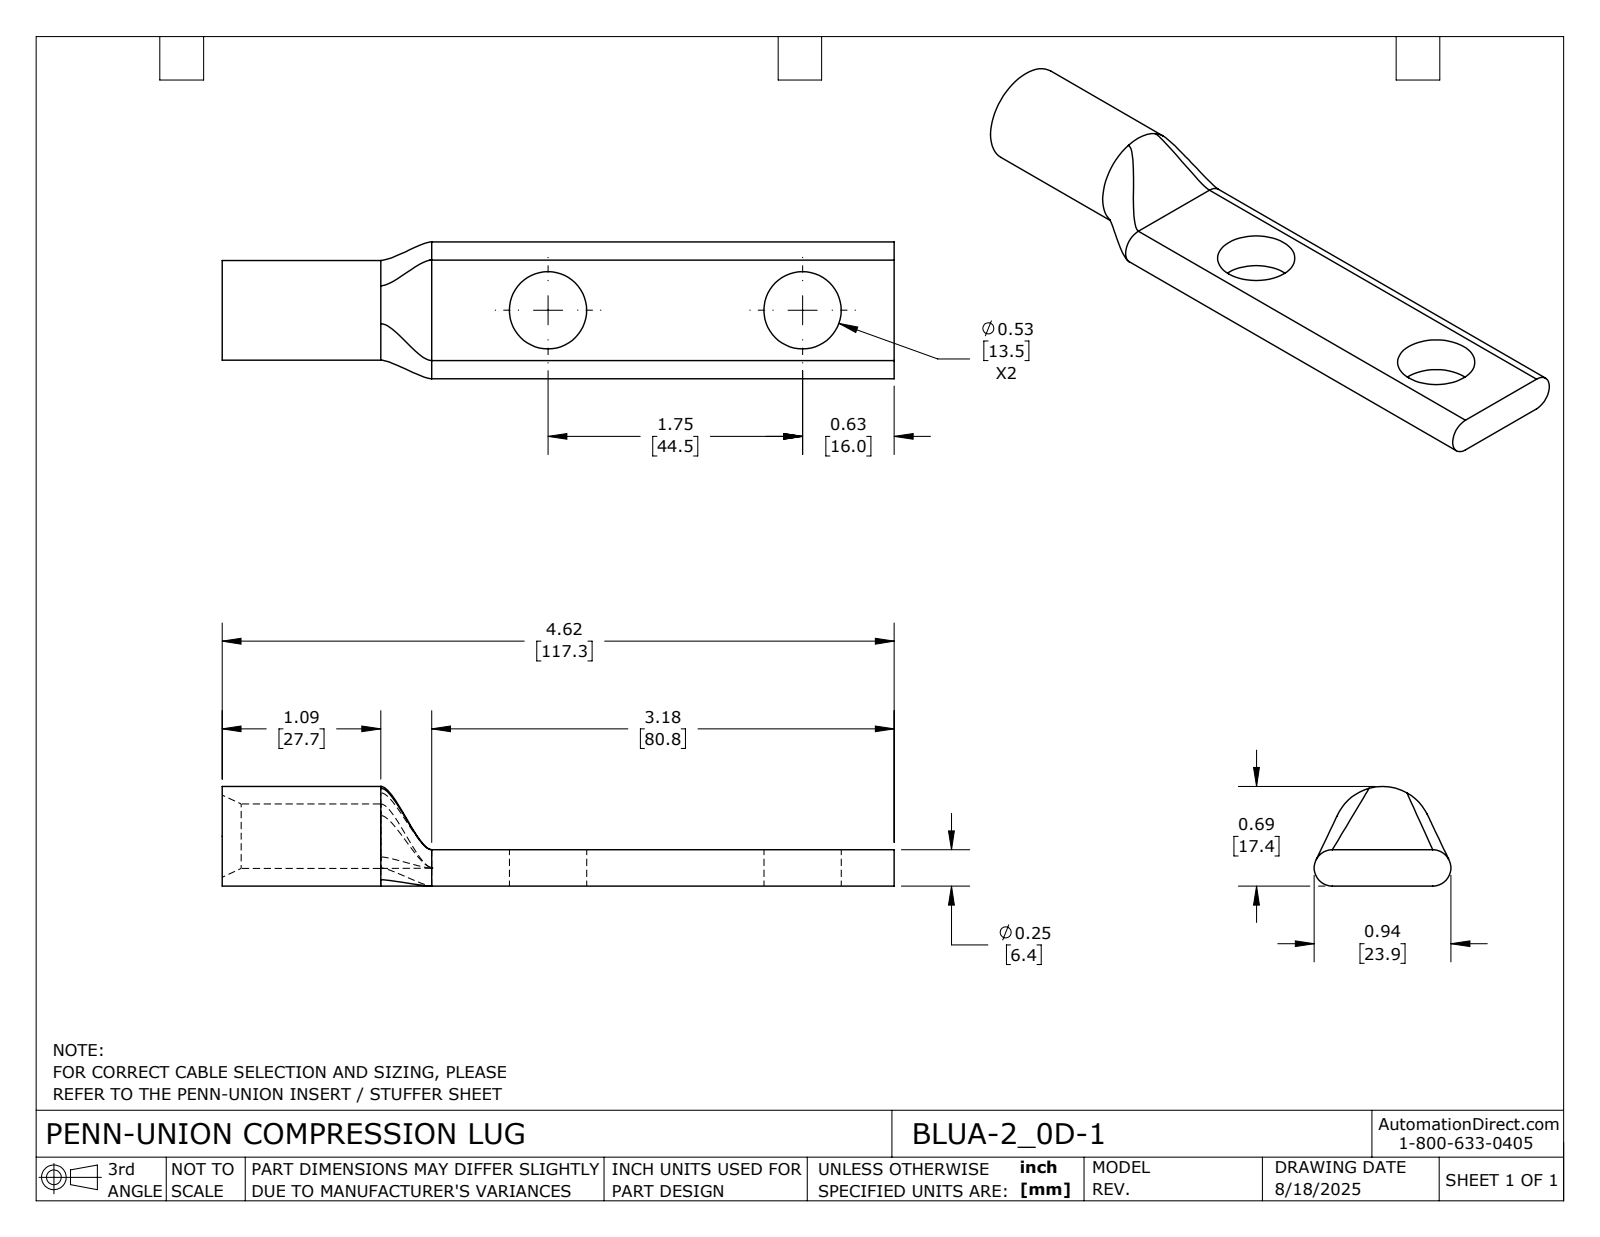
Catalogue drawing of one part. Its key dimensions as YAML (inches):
part_name: "BLUA-2_0D-1"
step_written_by: "SolidWorks 2024 (CONFIG_CONTROL_DESIGN)"
units: inches
bodies: {solids: 1, faces: 26, planar: 5, cylindrical: 11, other: 10}
overall_size: [4.62, 0.94, 0.685]
volume: 0.897
surface_area: 12.57
round_holes:
  - {diameter: 0.531, count: 2}
  - {diameter: 0.443, count: 1}
round_bosses_or_shafts:
  - {diameter: 0.685, count: 1}
partial_cylinders:
  - {radius: 0.125, count: 2}
face_to_face_distances: [0.25, 4.62, 1.44, 3.18]
hole_center_spacings: [1.75]
